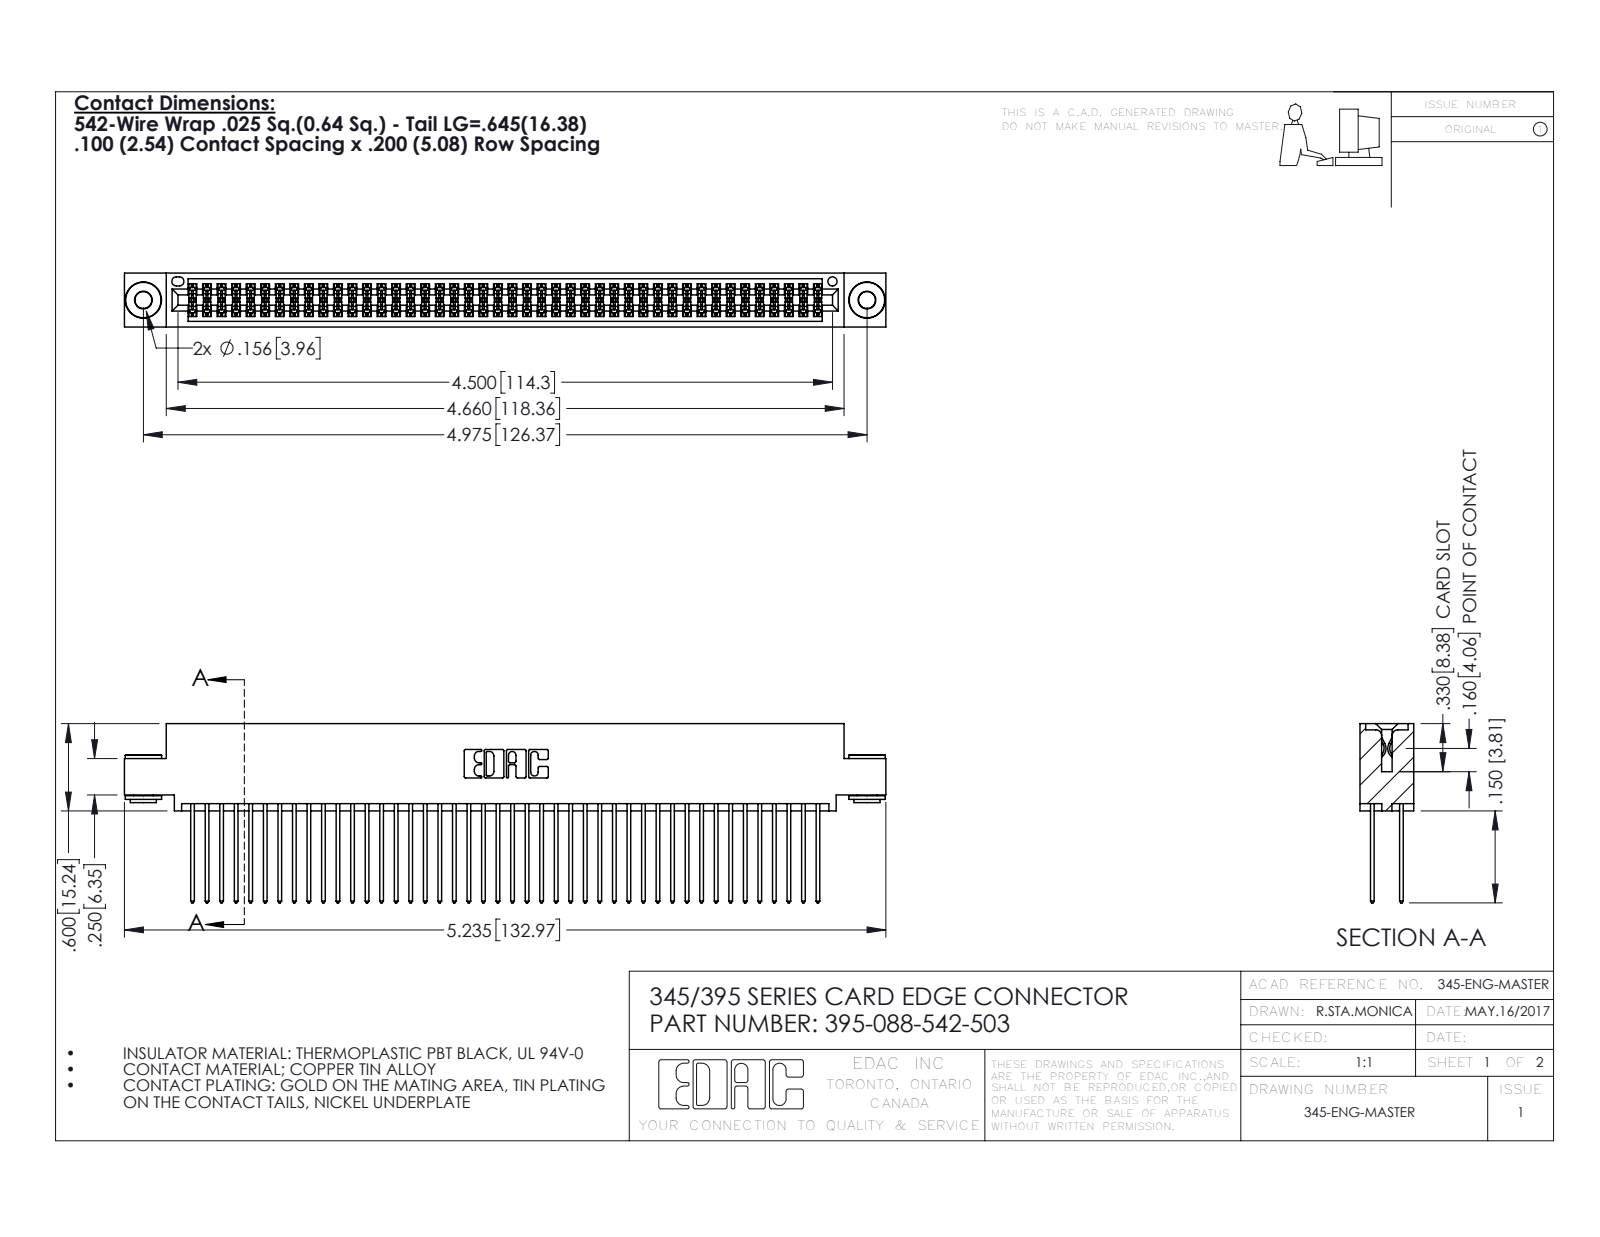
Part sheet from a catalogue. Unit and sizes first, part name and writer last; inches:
Units: inches
Overall size (bounding box): 5.235 × 1.232 × 0.37
Round holes (diameter × count): ⌀0.116 ×2, ⌀0.156 ×2, ⌀0.064 ×1
Round bosses / shafts (diameter × count): ⌀0.25 ×2, ⌀0.18 ×2, ⌀0.136 ×2
Partial cylindrical surfaces — rounded edges, fillets, slot ends (radius × count): R0.006 ×132, R0.01 ×88, R0.01 ×22, R0.007 ×6, R0.031 ×6, R0.026 ×3, R0.014 ×2, R0.019 ×2
Main face-to-face distances: 0.072, 0.298, 0.2, 0.025, 0.098, 0.272, 0.225, 0.37, 0.175, 0.149
Hole centre spacings: 0.27, 4.739, 4.975
Volume: 0.811 in³ · Surface area: 33.95 in²
Bodies: 91 solids, 4568 faces (2998 planar, 1562 cylindrical, 8 other)
Part name (STEP PRODUCT): 345-250-002_345-250-002-102; 395-088-542-503; 345-292-001_345-293-142; 345 Part_0.110 Offset - 0.156 Dia-TH
STEP written by: SolidWorks 2016 (CONFIG_CONTROL_DESIGN)
